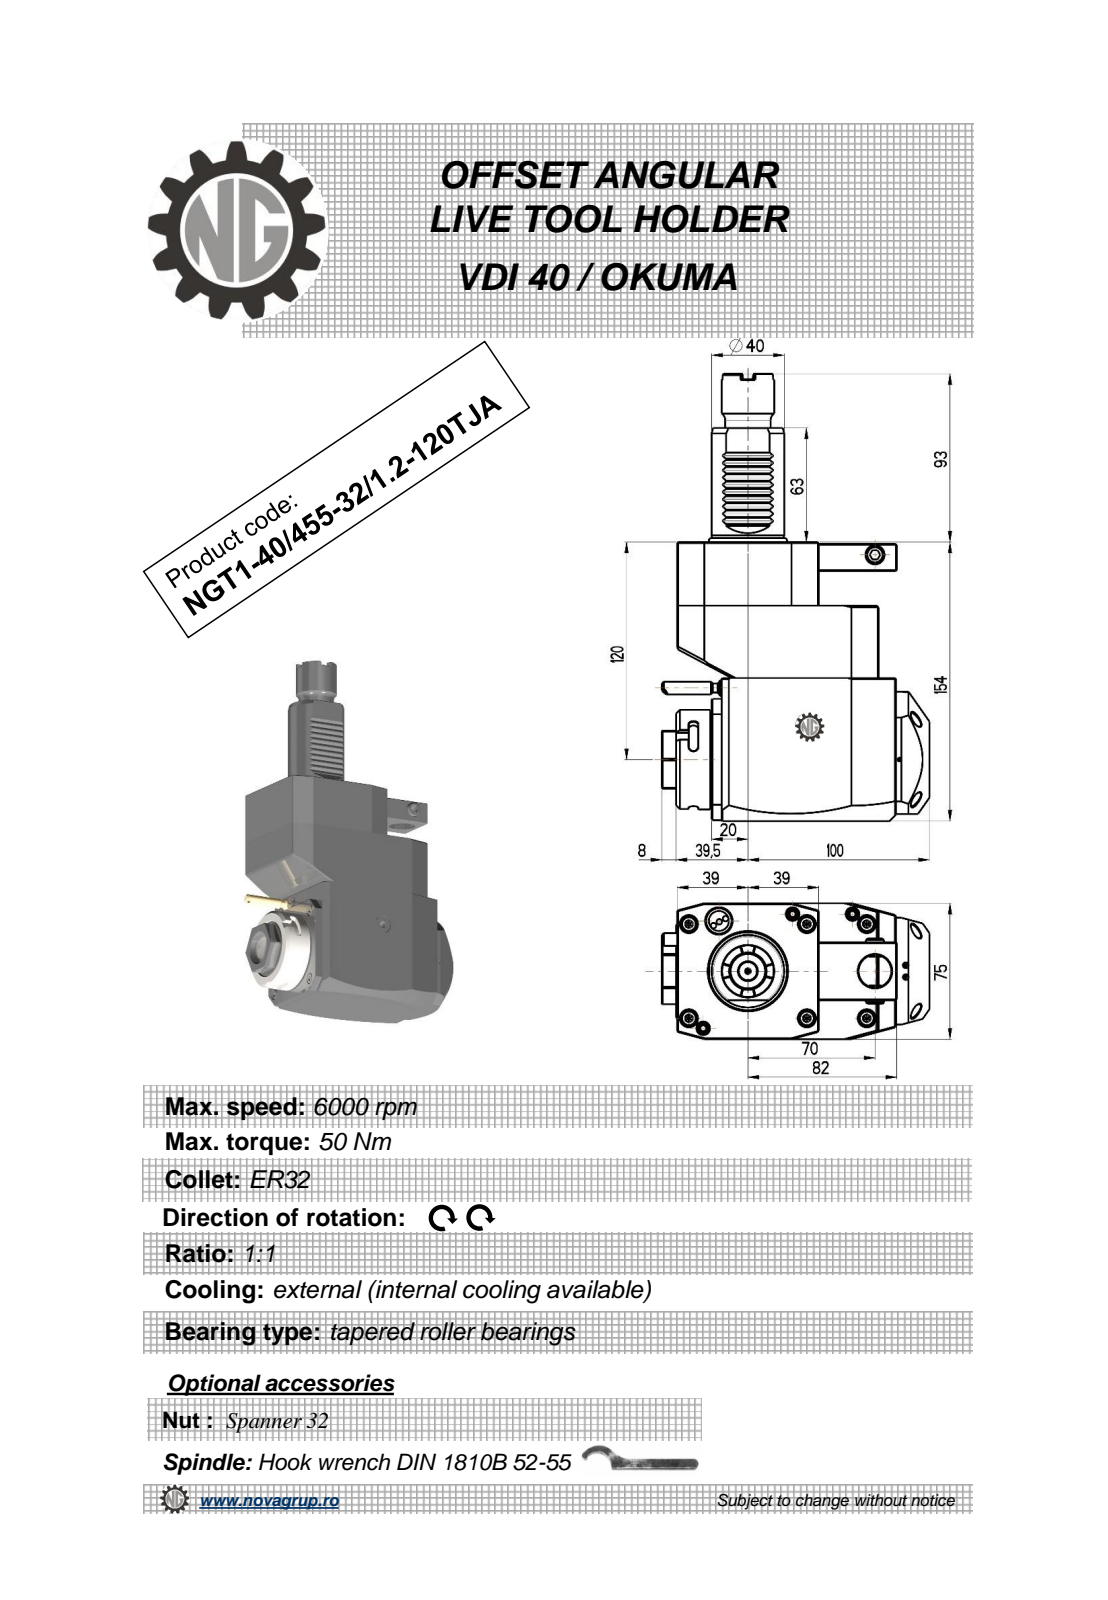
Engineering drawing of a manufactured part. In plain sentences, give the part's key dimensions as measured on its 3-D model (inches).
The part is named "NGT1_40_455_32_1_2_120TJA". Its 3-D file was written by "PRO/ENGINEER BY PARAMETRIC TECHNOLOGY CORPORATION, 2010280 (CONFIG_CONTROL_DESIGN)". It is 1 solid with 377 faces: 205 planar, 66 cylindrical and 106 other. Overall it measures 9.724 by 5.807 by 2.953 inches. Its volume is 79.15 cubic inches and its surface area 144.9 square inches. Round holes: 1 of diameter 0.098, 1 of diameter 0.118, 1 of diameter 0.374, 1 of diameter 0.709, 1 of diameter 0.906. Round bosses or shafts: 2 of diameter 0.353, 1 of diameter 2.165, 1 of diameter 1.89, 1 of diameter 1.575, 1 of diameter 1.142, 1 of diameter 0.984, 1 of diameter 0.394, 1 of diameter 0.276. Partial cylindrical surfaces (rounded edges, fillets, slot ends): 10 of radius 0.012, 6 of radius 0.098, 2 of radius 7.087, 1 of radius 0.02, 1 of radius 0.167, 1 of radius 0.394, 1 of radius 0.965, 1 of radius 1.476. The main face-to-face distances are 2.953, 6.063, 0.748, 2.323, 0.02, 4.37, 3.622, 1.378, 4.685, 2.106. The hole center spacings are 1.701, 2.956, 4.429.
